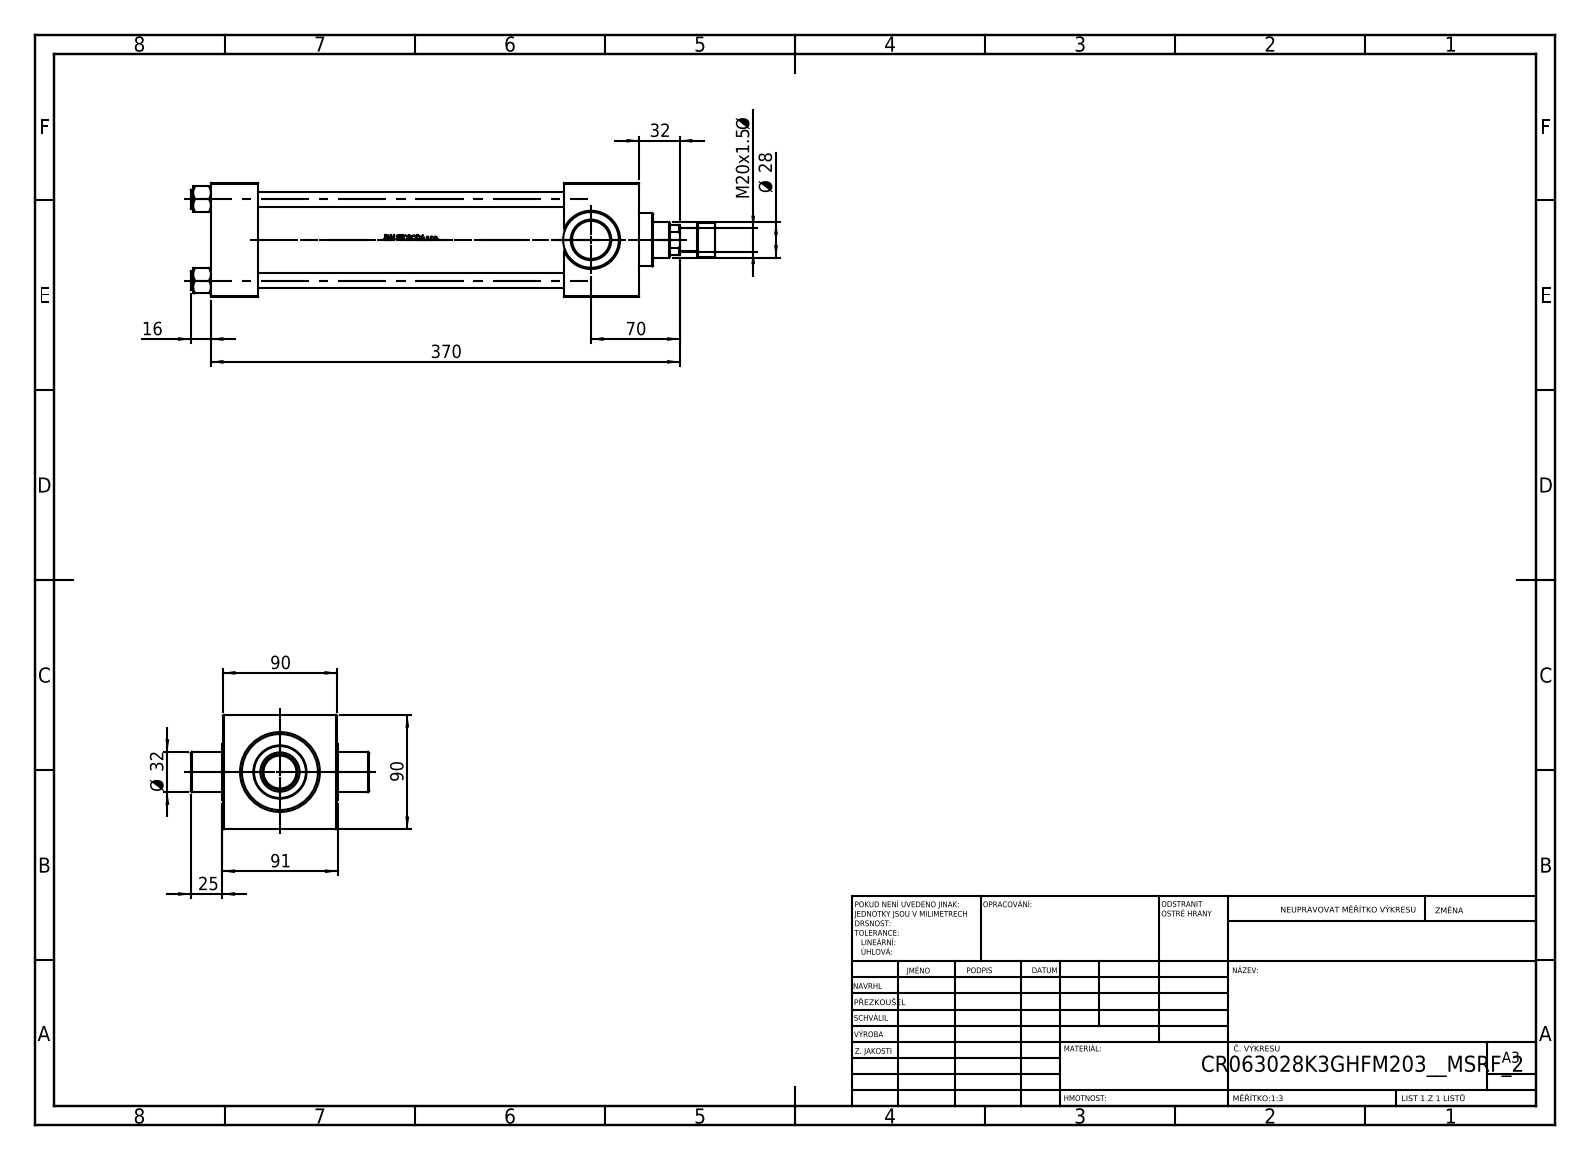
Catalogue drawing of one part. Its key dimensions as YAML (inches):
part_name: "V215CR_K_Body; V215_VC_A; V215CR_ROD_END_F; V215CR_K_TYCINKA (+2 more)"
step_written_by: "SolidWorks 2019 (CONFIG_CONTROL_DESIGN)"
units: inches
bodies: {solids: 12, faces: 1079, planar: 433, cylindrical: 116, other: 530}
overall_size: [16.299, 5.551, 3.543]
volume: 80.86
surface_area: 464.5
round_holes:
  - {diameter: 0.472, count: 4}
  - {diameter: 0.276, count: 1}
  - {diameter: 0.728, count: 1}
  - {diameter: 1.102, count: 1}
  - {diameter: 1.22, count: 1}
  - {diameter: 1.969, count: 1}
  - {diameter: 2.362, count: 1}
  - {diameter: 2.48, count: 1}
round_bosses_or_shafts:
  - {diameter: 0.591, count: 4}
  - {diameter: 2.717, count: 1}
  - {diameter: 1.654, count: 1}
  - {diameter: 1.26, count: 1}
  - {diameter: 1.063, count: 1}
  - {diameter: 0.709, count: 1}
partial_cylinders:
  - {radius: 0.866, count: 1}
face_to_face_distances: [3.543, 1.457, 0.02, 3.524, 13.307, 11.85, 9.528, 10.984, 2.323, 3.504]
hole_center_spacings: [1.79, 2.531, 3.58]
